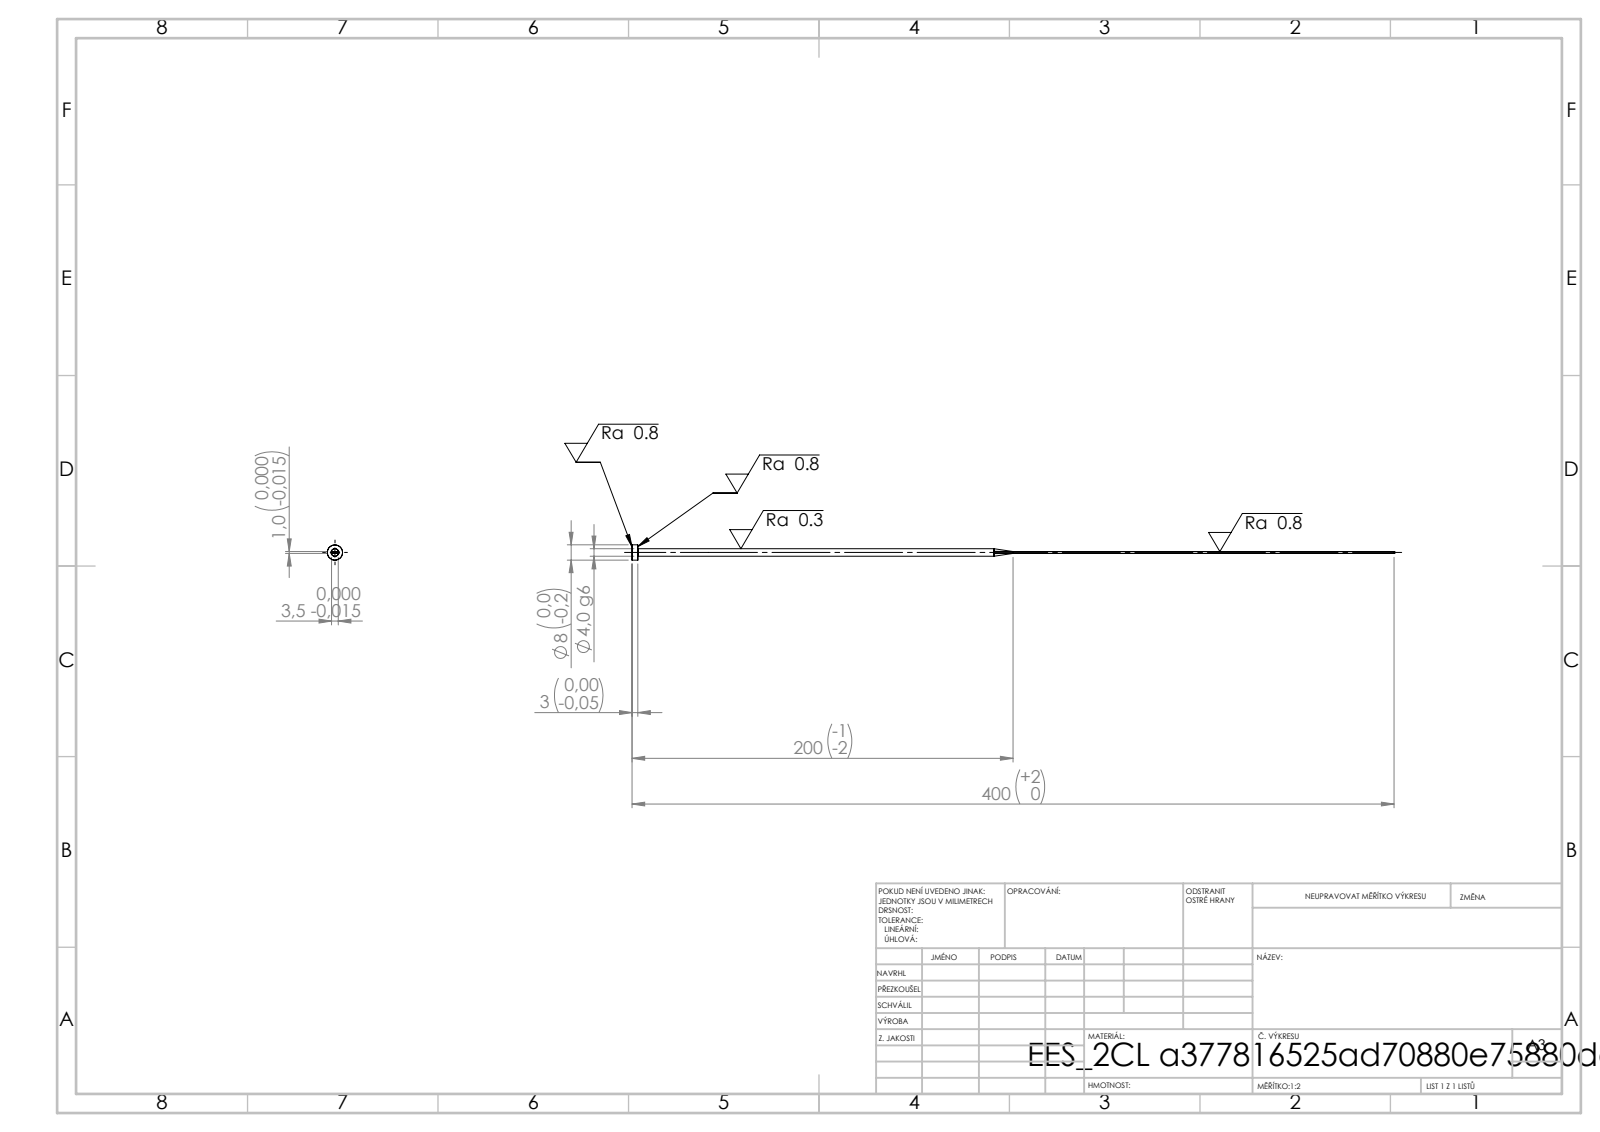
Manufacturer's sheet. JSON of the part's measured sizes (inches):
{"step_written_by": "SolidWorks 2019 (CONFIG_CONTROL_DESIGN)", "units": "inches", "bodies": {"solids": 1, "faces": 15, "planar": 7, "cylindrical": 4, "other": 4}, "overall_size": [15.748, 0.315, 0.315], "volume_in3": 0.2, "surface_area_in2": 6.853, "round_bosses_or_shafts": [[0.315, 1], [0.157, 1]], "face_to_face_distances": [0.039, 0.138, 0.118, 15.748, 15.63]}
